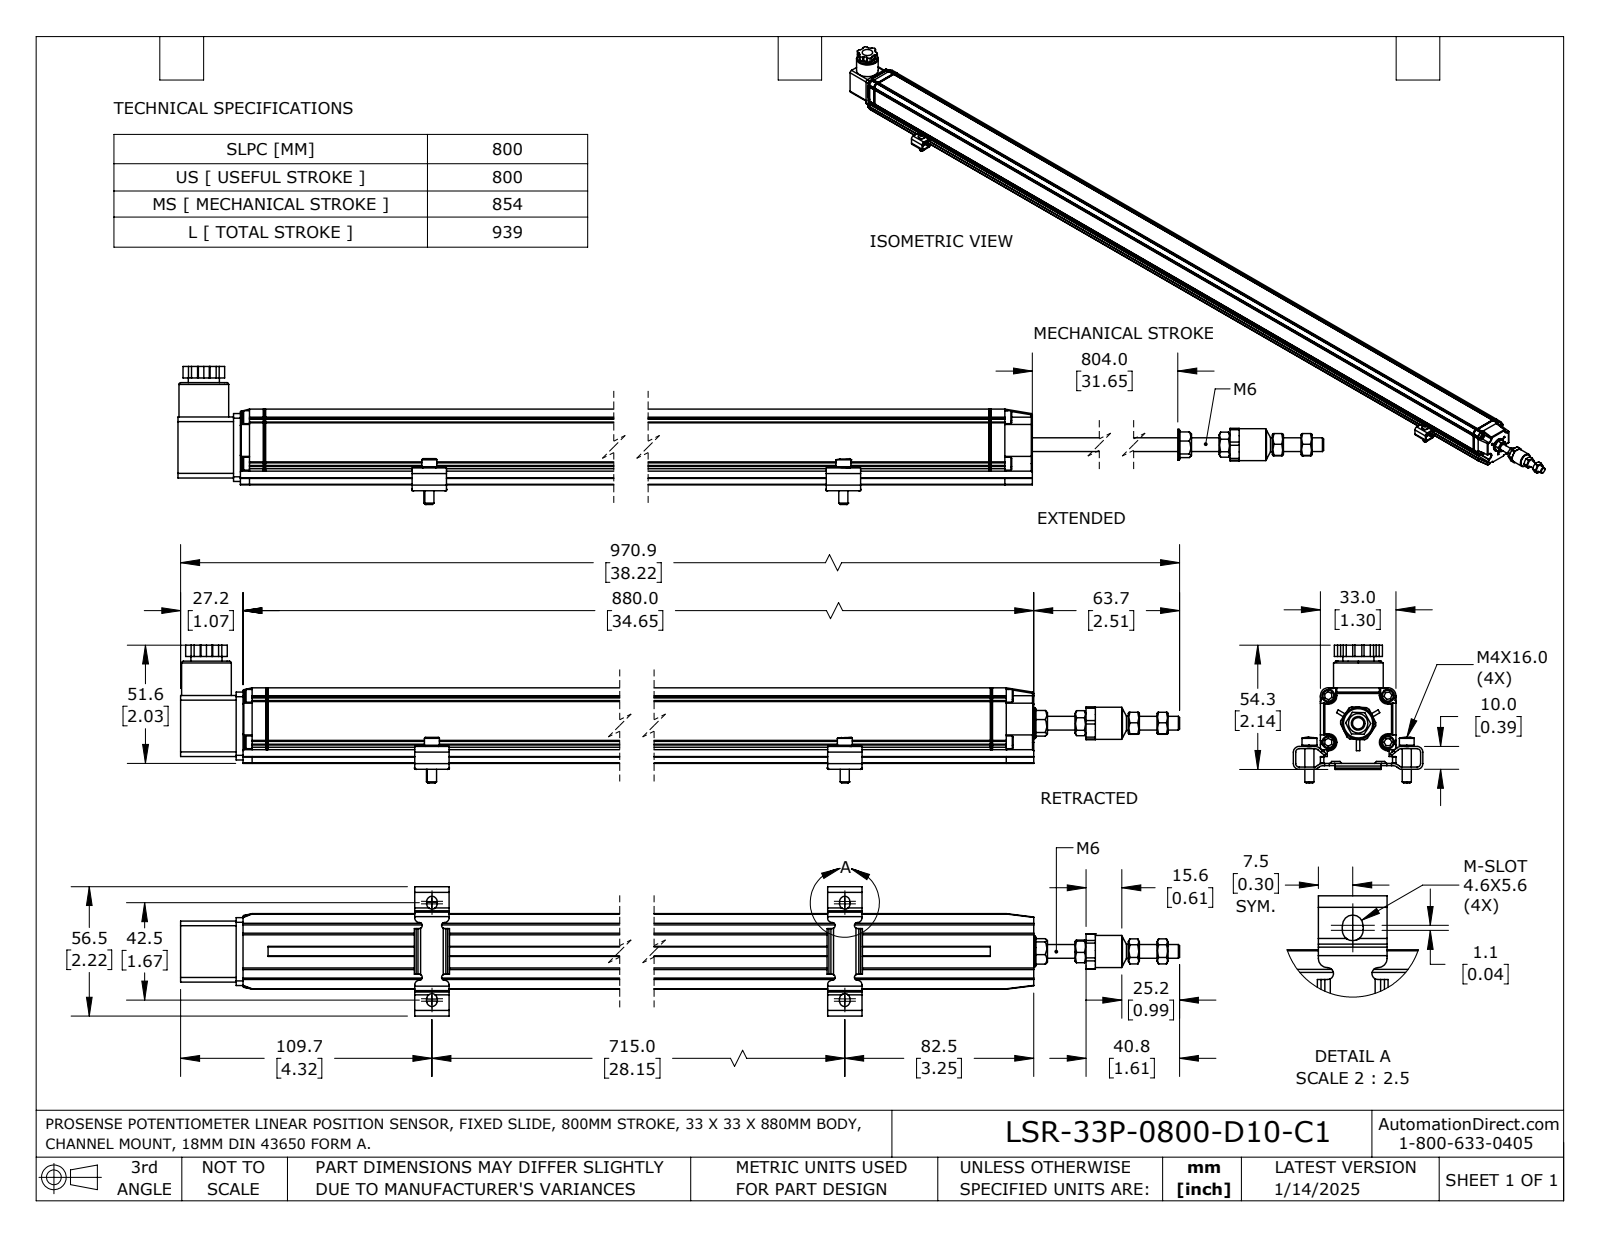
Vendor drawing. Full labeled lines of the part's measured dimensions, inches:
Part name (STEP PRODUCT): LSR-33P-0800-D10-C1
STEP written by: SolidWorks 2023 (AUTOMOTIVE_DESIGN)
Units: inches
Bodies: 14 solids, 995 faces (641 planar, 269 cylindrical, 85 other)
Overall size (bounding box): 38.222 × 2.37 × 2.224
Volume: 53.75 in³ · Surface area: 320.6 in²
Round holes (diameter × count): ⌀0.106 ×4, ⌀0.13 ×4, ⌀0.169 ×1, ⌀0.205 ×1, ⌀0.209 ×1, ⌀0.232 ×1, ⌀0.276 ×1, ⌀0.285 ×1, ⌀0.394 ×1, ⌀0.413 ×1, ⌀0.573 ×1, ⌀0.602 ×1
Round bosses / shafts (diameter × count): ⌀0.157 ×5, ⌀0.118 ×5, ⌀0.256 ×4, ⌀0.22 ×4, ⌀0.854 ×1, ⌀0.551 ×1, ⌀0.535 ×1, ⌀0.528 ×1
Partial cylindrical surfaces — rounded edges, fillets, slot ends (radius × count): R0.079 ×28, R0.02 ×23, R0.008 ×16, R0.051 ×8, R0.059 ×8, R0.089 ×8, R0.118 ×8, R0.039 ×4
Main face-to-face distances: 1.299, 0.118, 0.22, 1.181, 1.079, 0.039, 0.079, 0.142, 1.22, 0.185
Hole centre spacings: 0.047, 0.583, 0.607, 0.696, 0.73, 0.799, 1.024, 1.299
